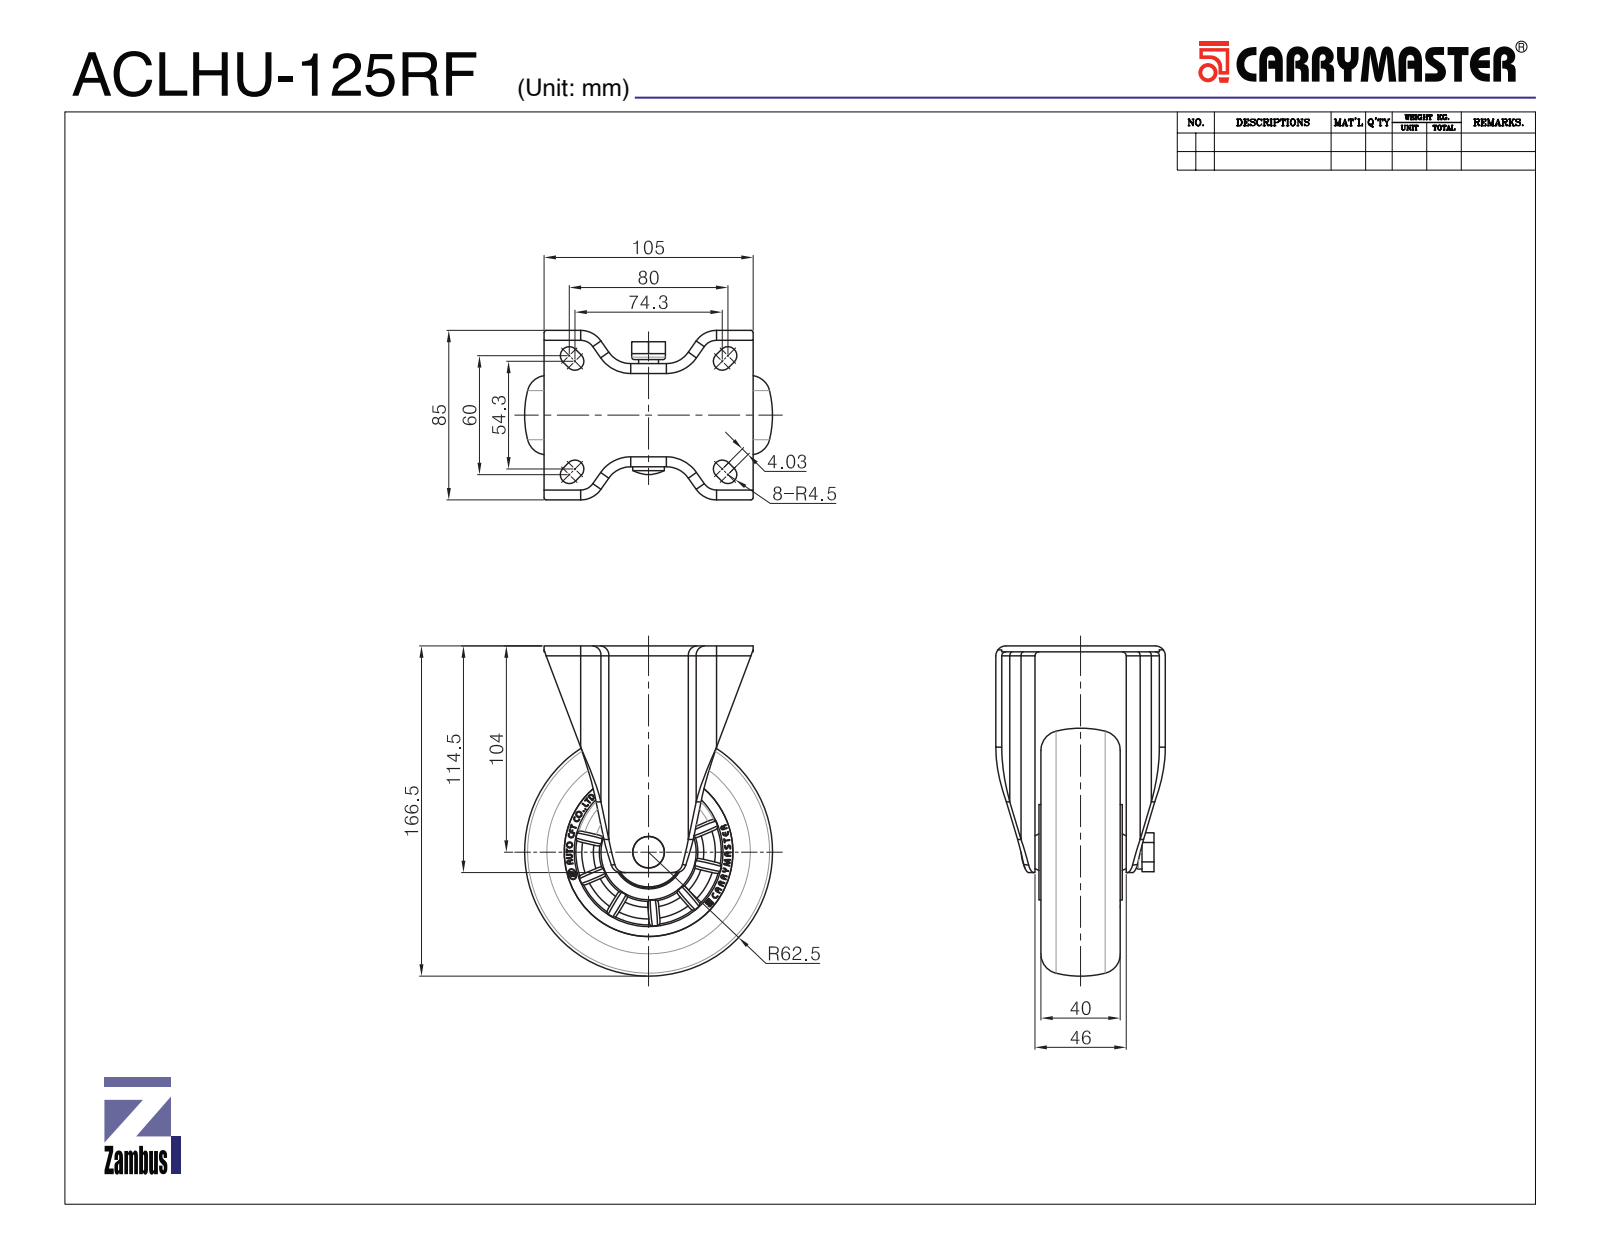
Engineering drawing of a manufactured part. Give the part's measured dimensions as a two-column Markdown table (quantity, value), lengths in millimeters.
| quantity | value |
| --- | --- |
| part name | ACLMU-125RF |
| STEP written by | SolidWorks 2015 (CONFIG_CONTROL_DESIGN) |
| units | millimeters |
| bodies | 7 solids, 1327 faces (729 planar, 188 cylindrical, 410 other) |
| overall size | 168.25 × 125 × 85.48 |
| volume | 510 993 mm³ |
| surface area | 154 289 mm² |
| round holes (diameter × count) | 1.7 × 2, 8.5 × 1, 10 × 1, 12 × 1, 30 × 1, 32 × 1, 85 × 1 |
| round bosses / shafts (diameter × count) | 0.65 × 2, 105 × 1, 35 × 1, 17 × 1 |
| partial cylindrical surfaces (radius × count) | 1 × 40, 12 × 20, 2 × 8, 4.5 × 8, 5 × 8, 9.5 × 4, 12.5 × 4, 13.5 × 4 |
| main face-to-face distances | 3, 6, 46, 40, 5, 41, 43, 49, 2, 1 |
| hole center spacings | 37.98, 40.78, 40.79 |
